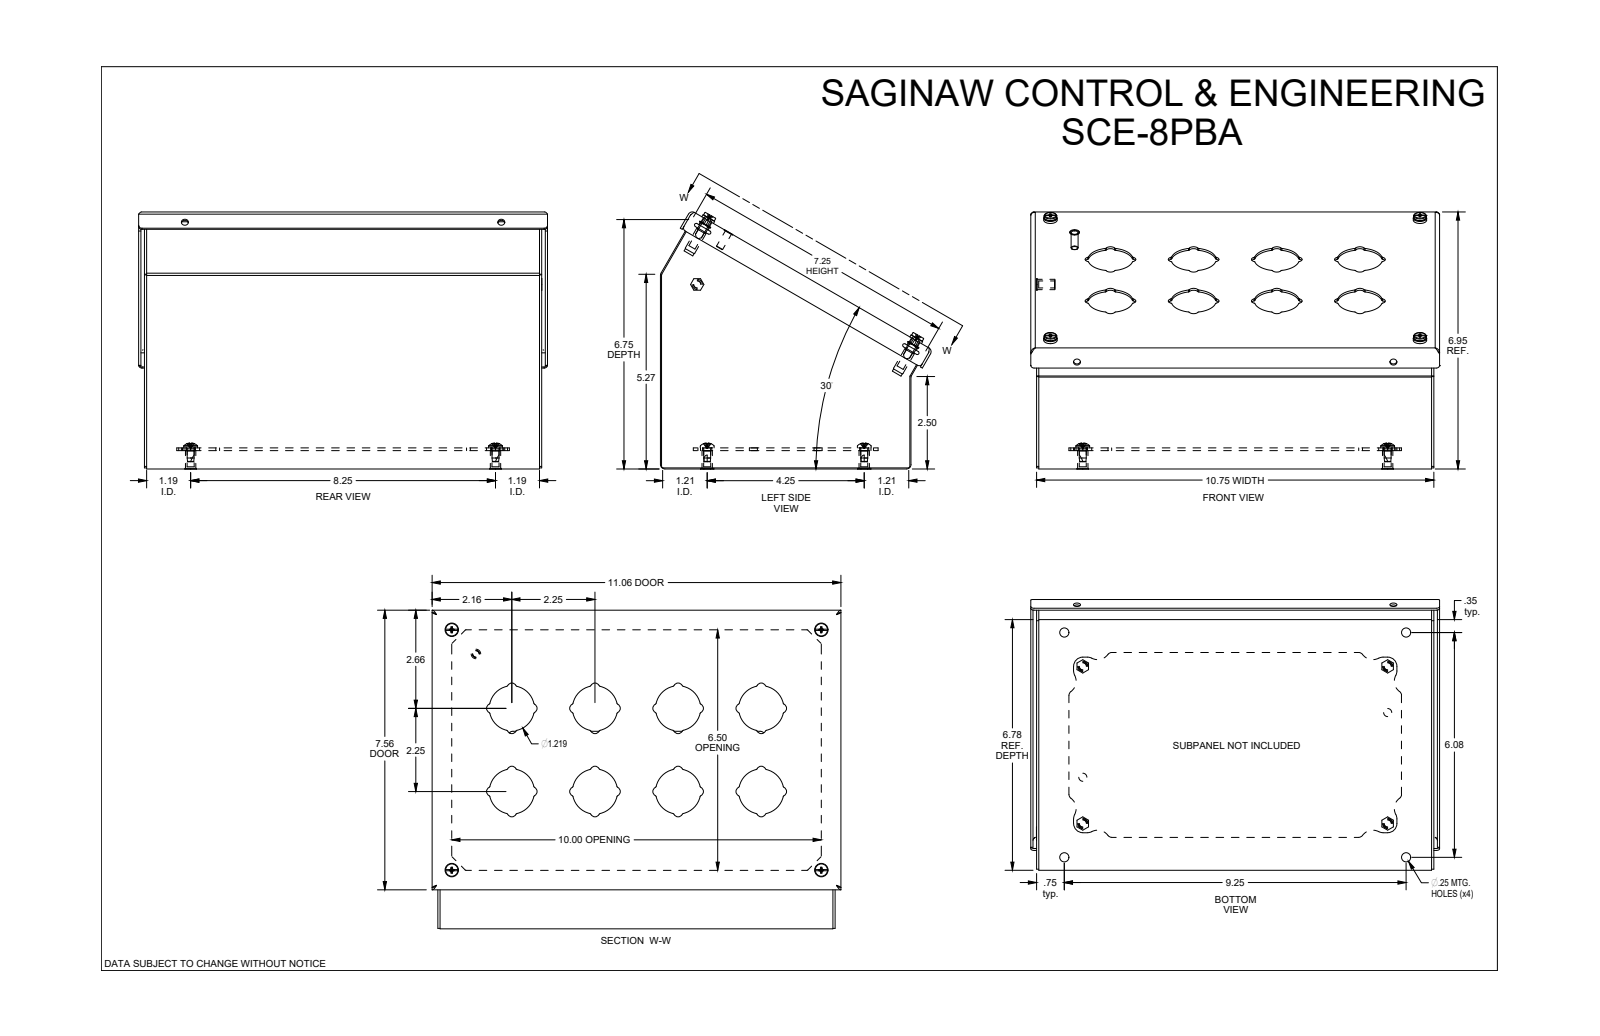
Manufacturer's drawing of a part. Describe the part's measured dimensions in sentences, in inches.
The part is named "SCE-8PBA". Its 3-D file was written by "SolidWorks 2021 (AUTOMOTIVE_DESIGN)". It is 3 solids with 613 faces: 193 planar, 342 cylindrical and 78 other. Overall it measures 11.063 by 7.345 by 6.978 inches. Its volume is 25.35 cubic inches and its surface area 830.1 square inches. Round holes: 12 of diameter 0.25, 9 of diameter 0.19, 4 of diameter 0.22, 4 of diameter 0.266, 4 of diameter 0.317, 2 of diameter 0.218, 1 of diameter 0.187. Round bosses or shafts: 5 of diameter 0.28, 4 of diameter 0.362, 4 of diameter 0.34, 4 of diameter 0.292, 4 of diameter 0.27, 4 of diameter 0.26, 1 of diameter 0.256, 1 of diameter 0.188. Partial cylindrical surfaces (rounded edges, fillets, slot ends): 64 of radius 0.04, 40 of radius 0.125, 12 of radius 0.25, 8 of radius 0.01, 8 of radius 0.03, 8 of radius 0.06, 8 of radius 0.115, 8 of radius 0.24. The main face-to-face distances are 0.06, 10.63, 6.72, 0.436, 0.496, 0.571, 0.511, 0.075, 10.69, 10.57. The hole center spacings are 10, 6.5, 6.505, 11.929, 9.94, 10, 11.927, 6.505.
